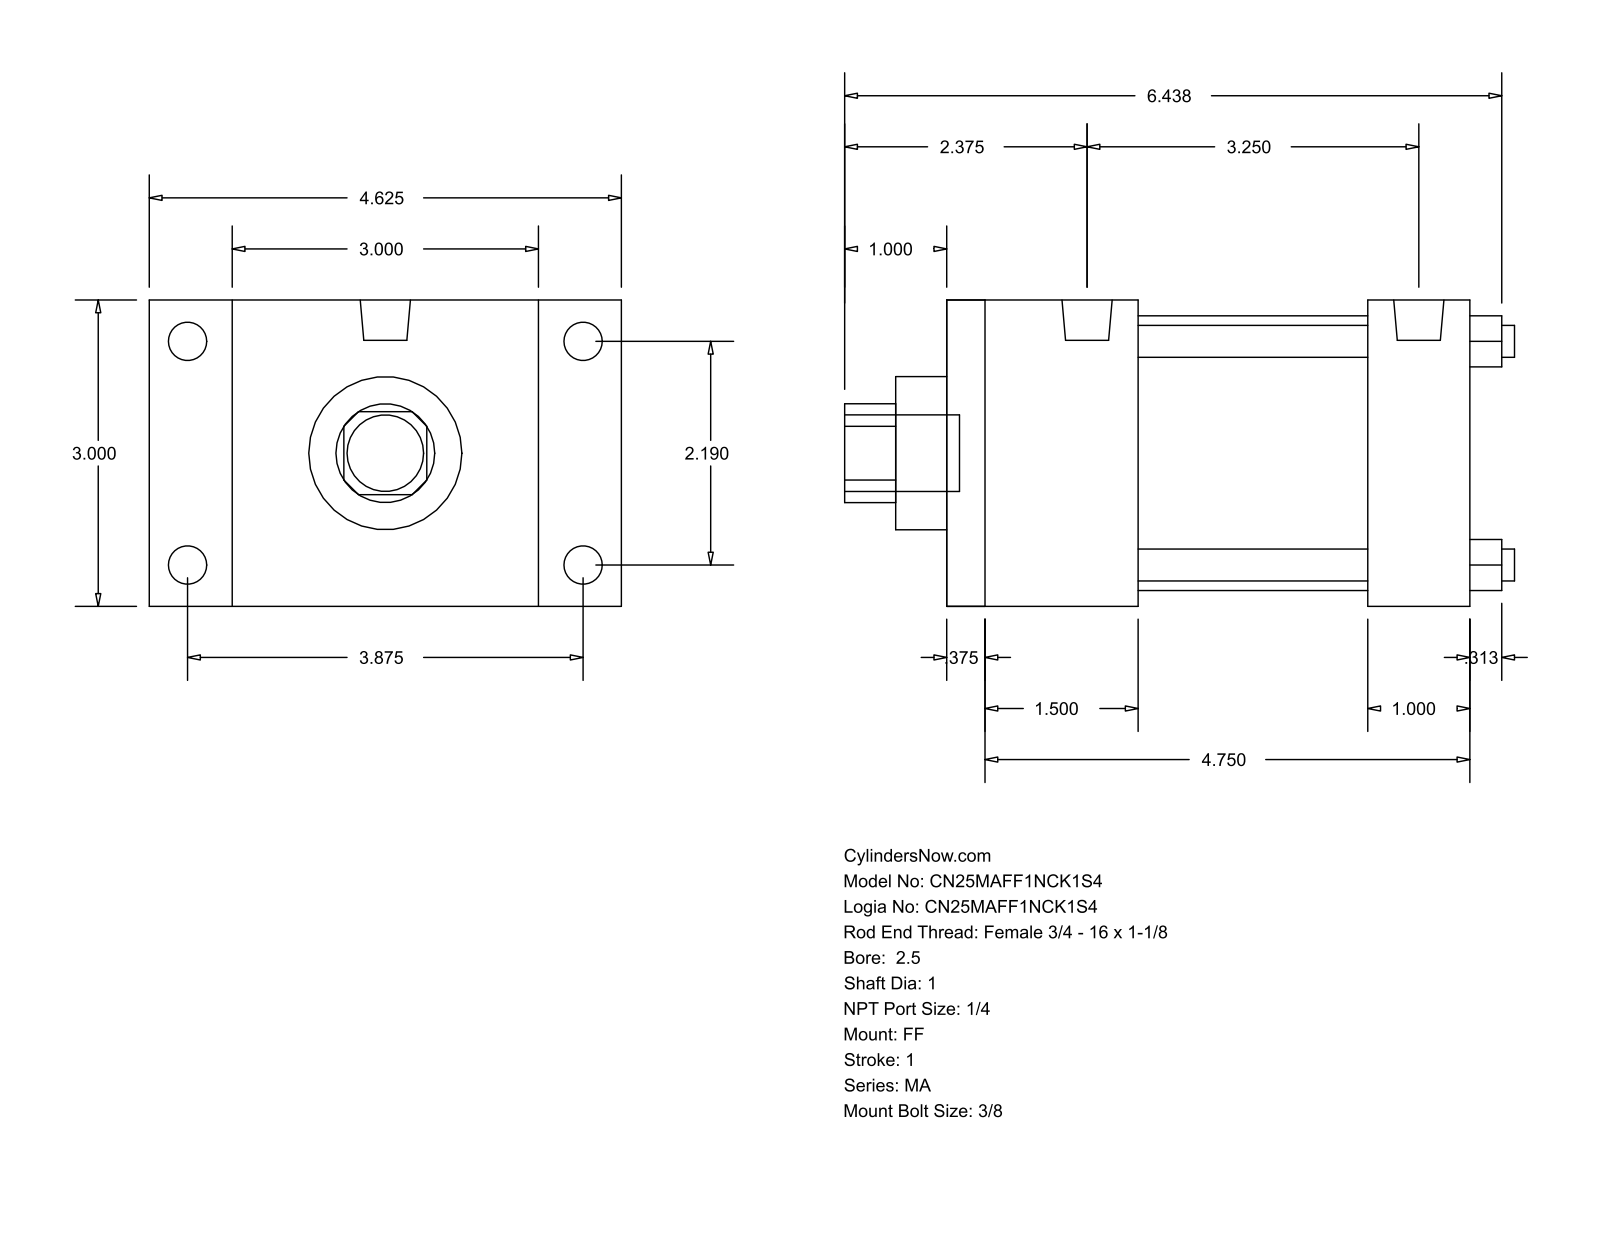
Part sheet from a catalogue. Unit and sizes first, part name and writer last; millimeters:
Units: millimetres
Overall size (bounding box): 166.69 × 117.47 × 76.2
Round holes (diameter × count): ⌀7.94 ×4, ⌀25.4 ×1, ⌀38.1 ×1, ⌀68.33 ×1
Round bosses / shafts (diameter × count): ⌀9.53 ×4, ⌀7.94 ×4, ⌀12.49 ×2, ⌀19.05 ×1
Partial cylindrical surfaces — rounded edges, fillets, slot ends (radius × count): R12.29 ×1
Main face-to-face distances: 76.2, 130.17, 120.65, 9.52, 25.39, 47.63, 104.78, 38.11, 95.26, 57.15
Hole centre spacings: 39.33, 55.62, 78.66
Bodies: 0 solids, 92 faces (64 planar, 28 cylindrical, 0 other)
Part name (STEP PRODUCT): MA_FF__0250_1
STEP written by: GSSL Pune (CONFIG_CONTROL_DESIGN)
